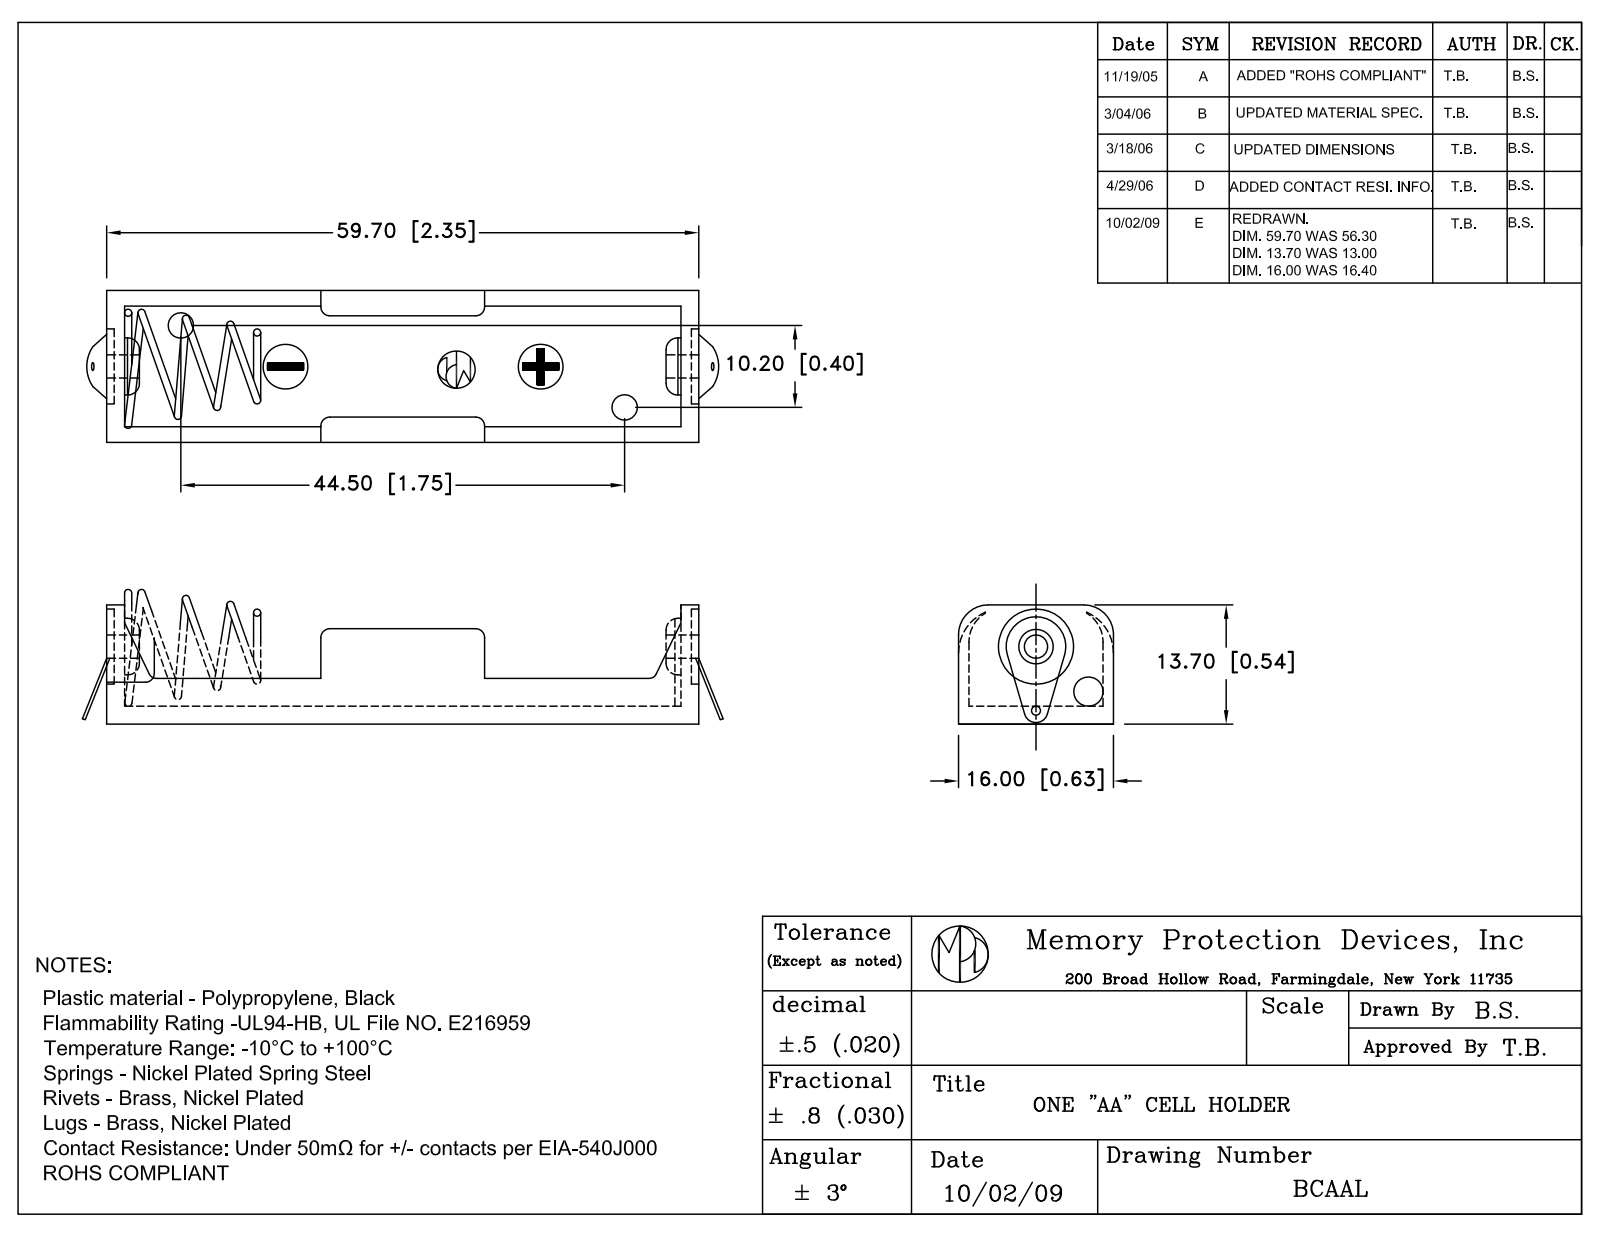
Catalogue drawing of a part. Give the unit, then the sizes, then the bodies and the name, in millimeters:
Units: millimetres
Overall size (bounding box): 67.89 × 16 × 13.7
Round holes (diameter × count): ⌀0.7 ×2, ⌀2.5 ×2, ⌀1.6 ×1, ⌀2.3 ×1, ⌀2.54 ×1, ⌀3 ×1, ⌀8 ×1
Round bosses / shafts (diameter × count): ⌀3.7 ×2, ⌀6.2 ×1, ⌀0.6 ×1
Partial cylindrical surfaces — rounded edges, fillets, slot ends (radius × count): R0.2 ×12, R2 ×4, R1.5 ×2, R3 ×2, R4.21 ×2, R6.2 ×2, R8 ×2, R8.31 ×2
Main face-to-face distances: 1.1, 1.55, 14.9, 16, 58.6, 13.8, 57.5, 59.7, 0.31, 59.39
Hole centre spacings: 8.16, 8.18, 45.65
Volume: 2 726 mm³ · Surface area: 4 992 mm²
Bodies: 3 solids, 204 faces (79 planar, 79 cylindrical, 46 other)
Part name (STEP PRODUCT): BCAAL
STEP written by: SolidWorks 2017 (AUTOMOTIVE_DESIGN)
